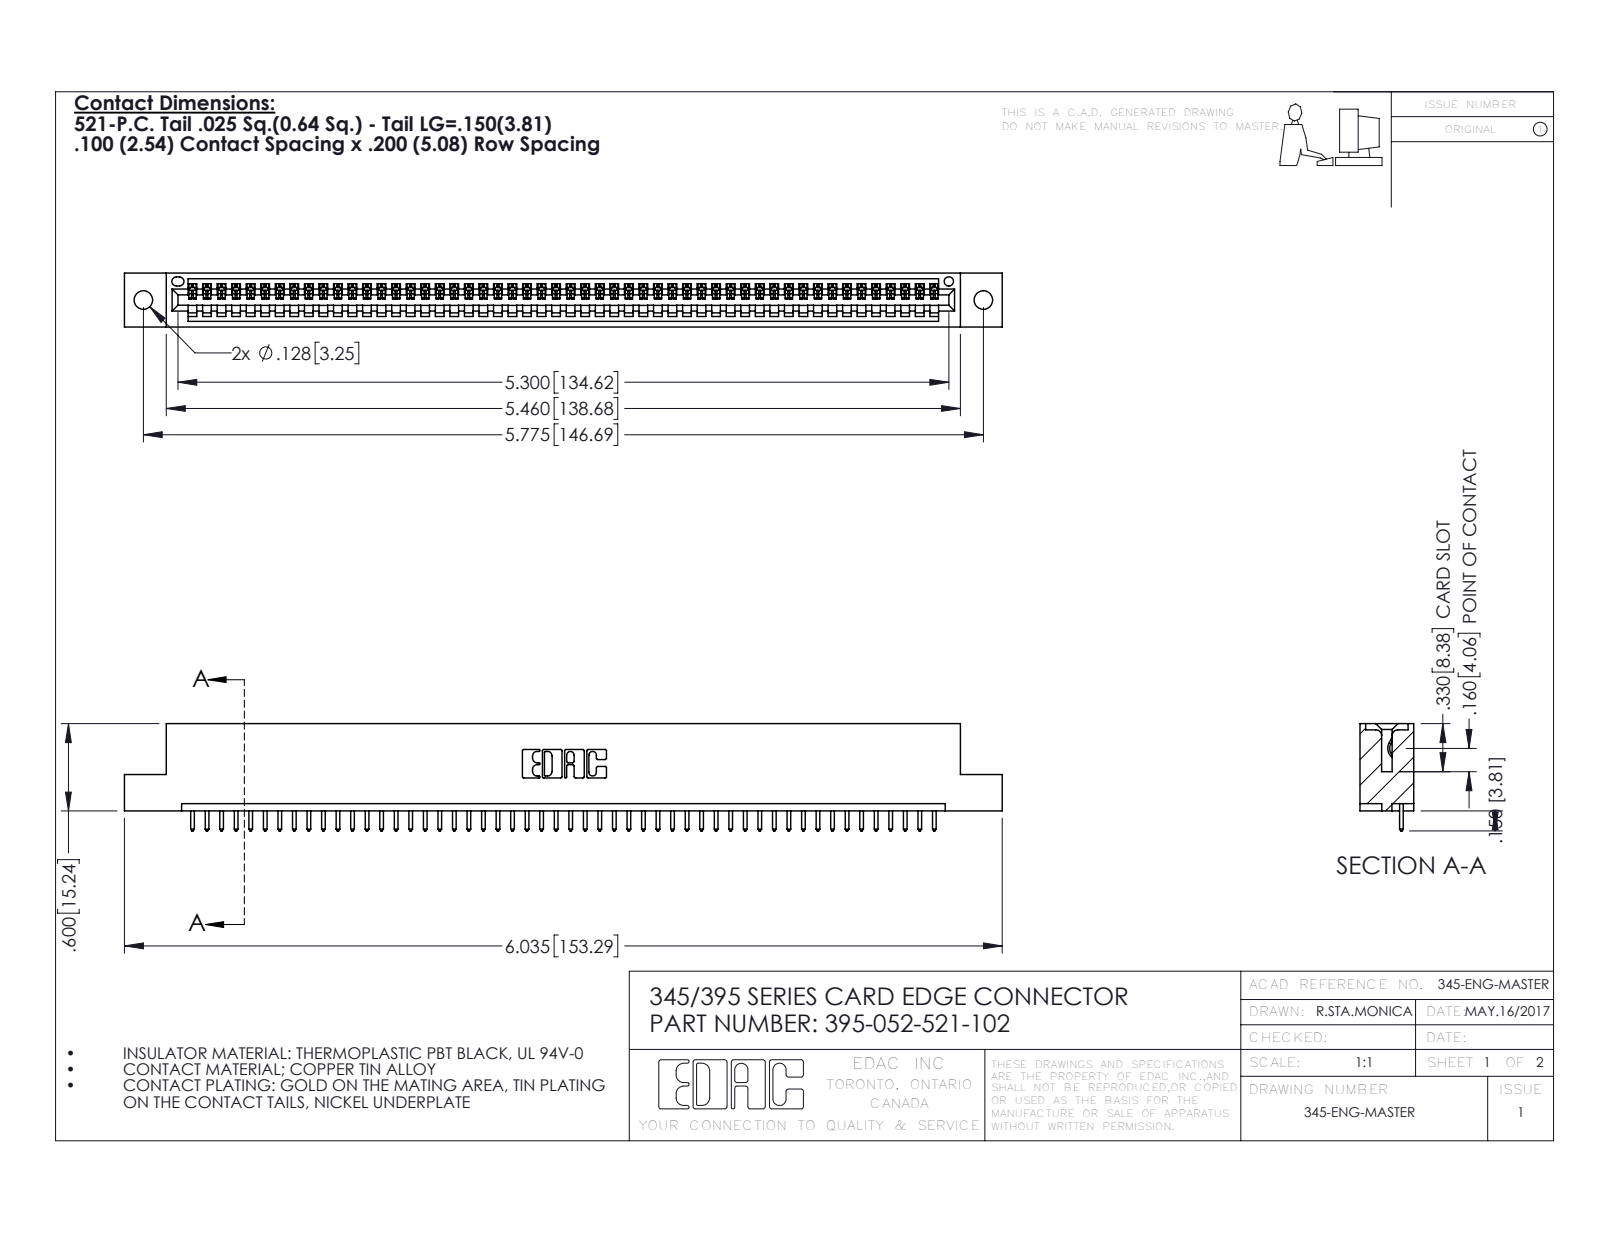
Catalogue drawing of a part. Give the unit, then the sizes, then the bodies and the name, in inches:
Units: inches
Overall size (bounding box): 6.035 × 0.737 × 0.37
Round holes (diameter × count): ⌀0.128 ×2, ⌀0.064 ×1
Partial cylindrical surfaces — rounded edges, fillets, slot ends (radius × count): R0.006 ×104, R0.01 ×104, R0.01 ×22, R0.007 ×6, R0.031 ×6, R0.026 ×3, R0.031 ×2, R0.04 ×2
Main face-to-face distances: 0.298, 0.072, 0.37, 0.2, 0.098, 0.272, 0.025, 0.225, 0.149, 0.072
Hole centre spacings: 0.27, 5.539, 5.775
Volume: 0.882 in³ · Surface area: 28.67 in²
Bodies: 53 solids, 3142 faces (2160 planar, 982 cylindrical, 0 other)
Part name (STEP PRODUCT): 395-052-521-102; 345 Part_Flush Mounting Lugs - 0.128 Dia; 345-292-001_345-293-121
STEP written by: SolidWorks 2016 (CONFIG_CONTROL_DESIGN)
